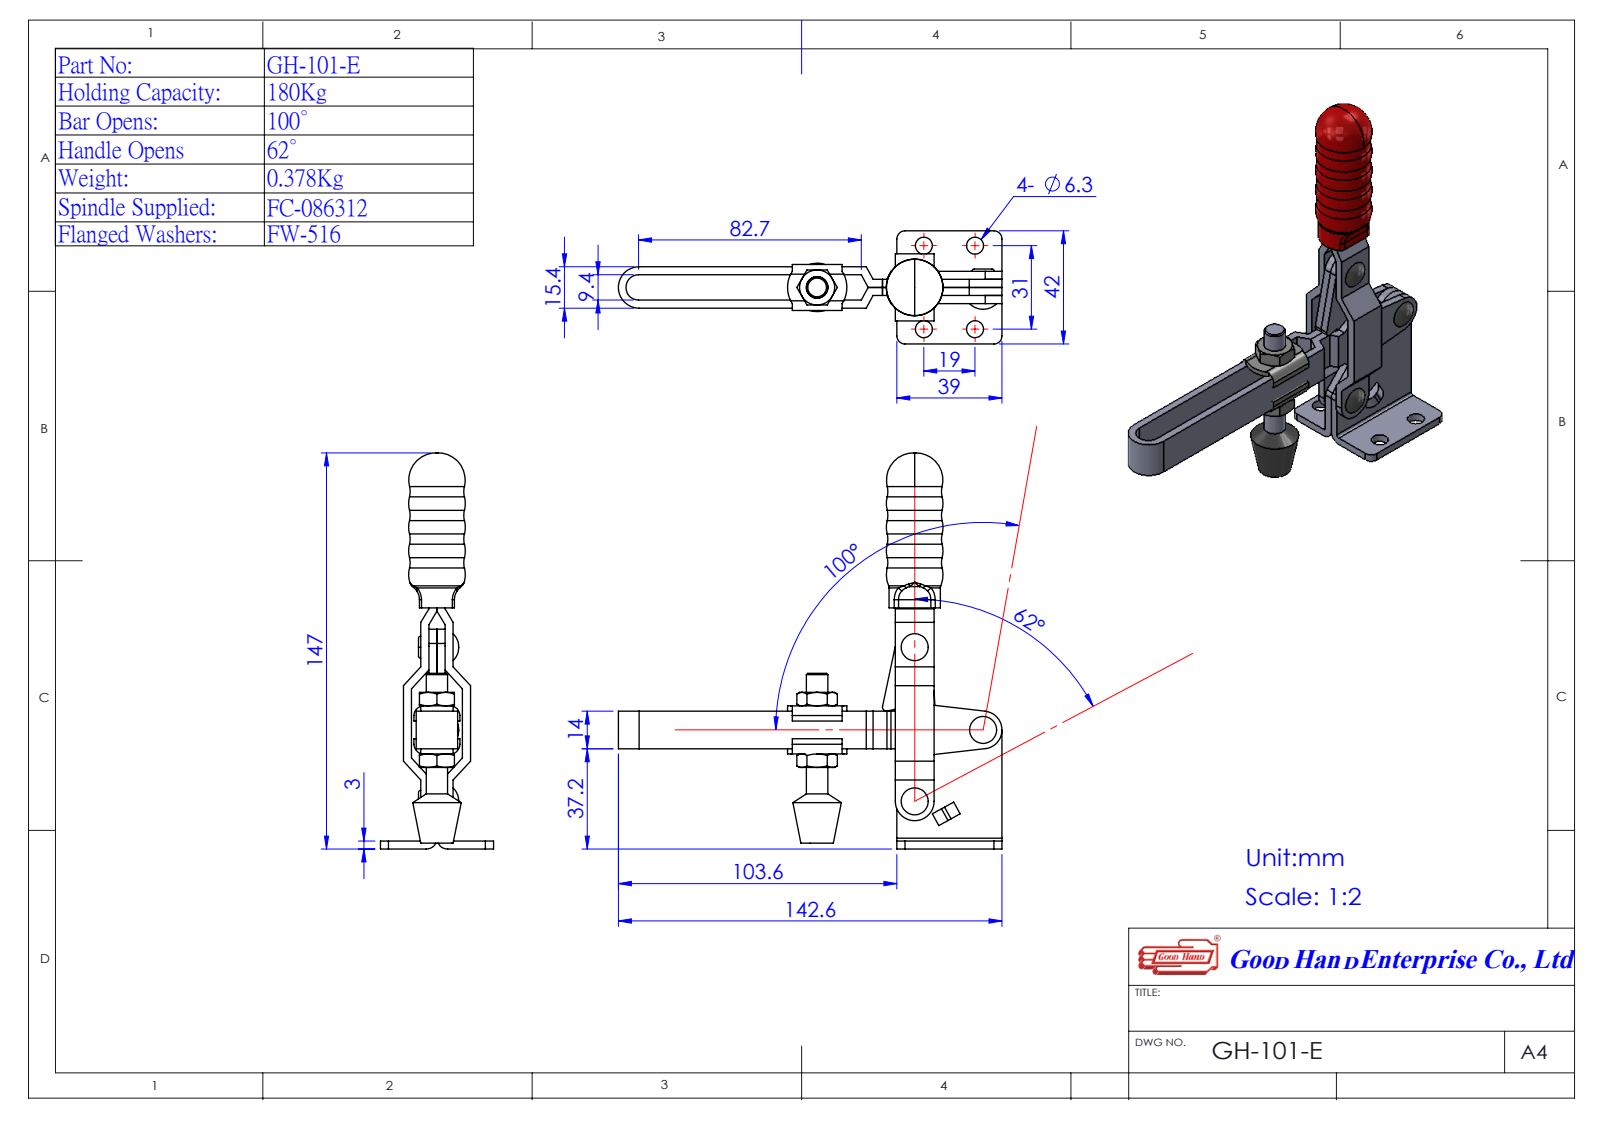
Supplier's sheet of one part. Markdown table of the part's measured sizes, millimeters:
| quantity | value |
| --- | --- |
| part name | Group4^GH-101-D(簡化); Group6^GH-101-E(簡化); GH-101-E(簡化); Group3^GH-101-E(簡化) (+2 more) |
| STEP written by | SolidWorks 2016 (AUTOMOTIVE_DESIGN) |
| units | millimeters |
| bodies | 5 solids, 321 faces (136 planar, 91 cylindrical, 94 other) |
| overall size | 147.01 × 142.4 × 42 |
| volume | 62 581 mm³ |
| surface area | 34 200 mm² |
| round holes (diameter × count) | 5 × 4, 6.3 × 4 |
| round bosses / shafts (diameter × count) | 6.3 × 2, 7.93 × 1 |
| partial cylindrical surfaces (radius × count) | 3 × 6, 1.2 × 4, 2 × 4, 3.6 × 4, 4 × 2, 6 × 2, 6.75 × 2, 11.04 × 2 |
| main face-to-face distances | 3, 10.7, 1.7, 6, 4.7, 7.7, 12.4, 13.7, 1.3, 9 |
| hole center spacings | 19, 31, 36.36, 24.2, 26.53, 30.72, 36.71, 39.85 |
